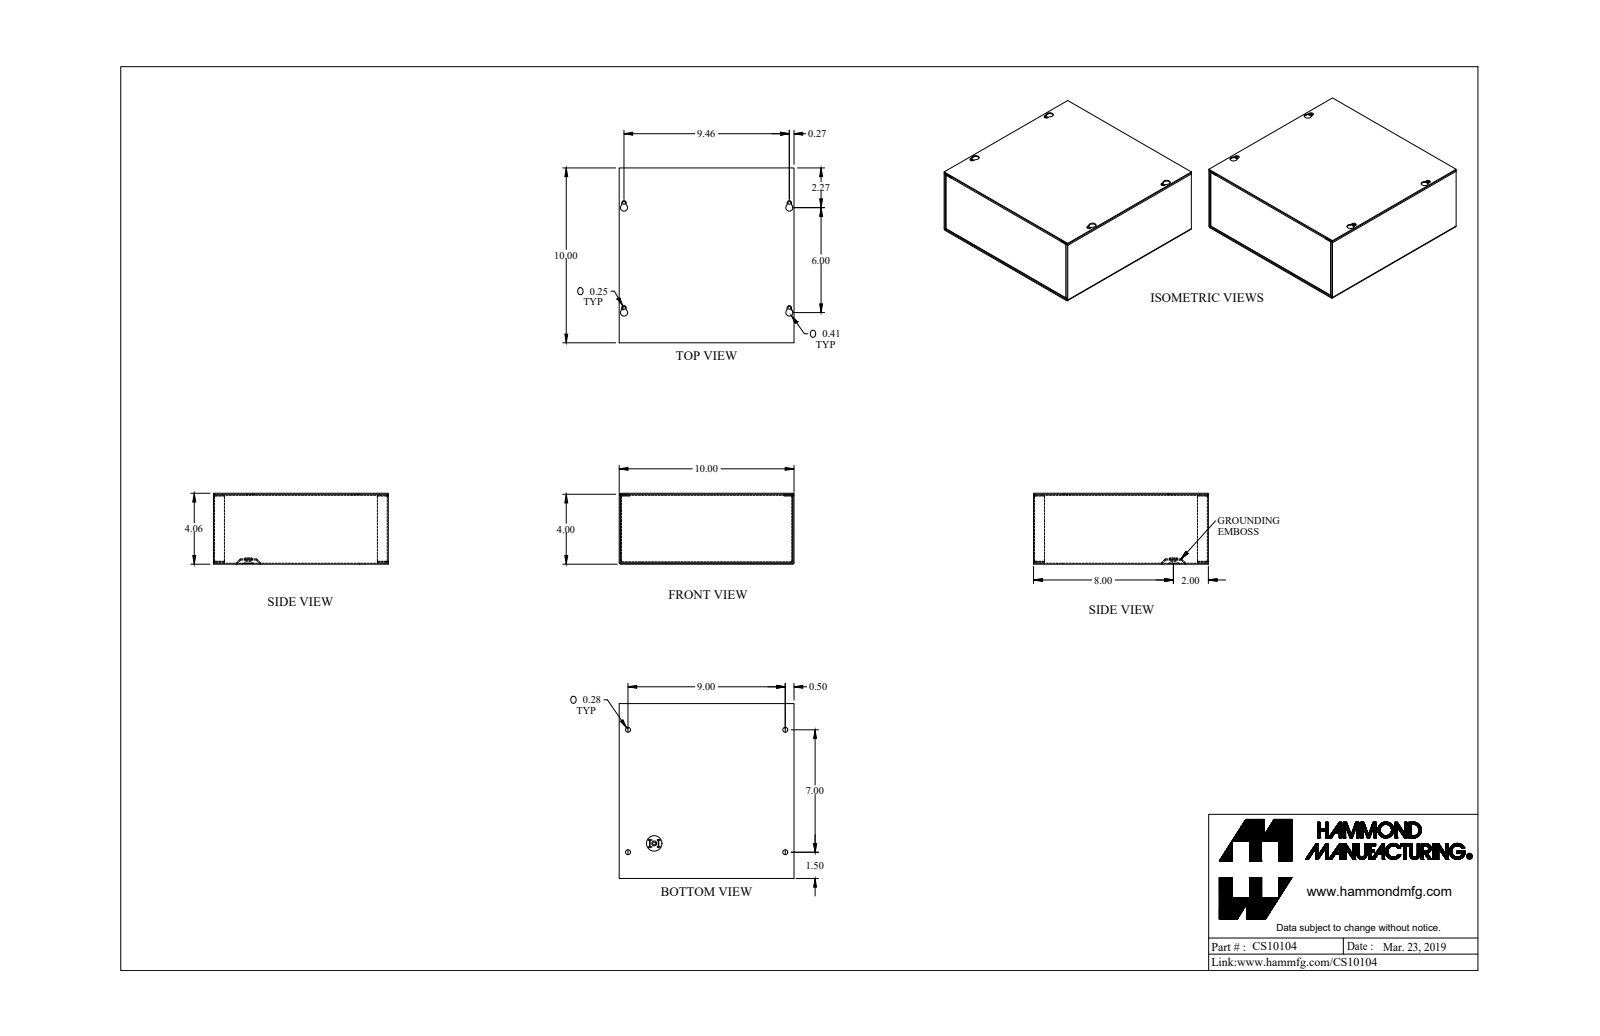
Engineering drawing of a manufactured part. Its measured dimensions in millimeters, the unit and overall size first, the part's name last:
Units: millimetres
Overall size (bounding box): 254 × 254 × 103
Round holes (diameter × count): ⌀4.3 ×5, ⌀7.1 ×4, ⌀12.7 ×1
Round bosses / shafts (diameter × count): ⌀12.5 ×1, ⌀7.2 ×1
Partial cylindrical surfaces — rounded edges, fillets, slot ends (radius × count): R0.7 ×12, R2.2 ×12, R1.4 ×8, R3.2 ×4, R5.2 ×4
Main face-to-face distances: 1.4, 101.6, 252.6, 100.2, 103, 254, 251.1, 2, 98.1, 99.6
Hole centre spacings: 14, 165.2, 234.8, 286.7, 152.4, 177.8, 228.6, 240.3
Volume: 363 600 mm³ · Surface area: 508 700 mm²
Bodies: 4 solids, 205 faces (125 planar, 72 cylindrical, 8 other)
Part name (STEP PRODUCT): CS10104_Default
STEP written by: SolidWorks 2019 (CONFIG_CONTROL_DESIGN)
